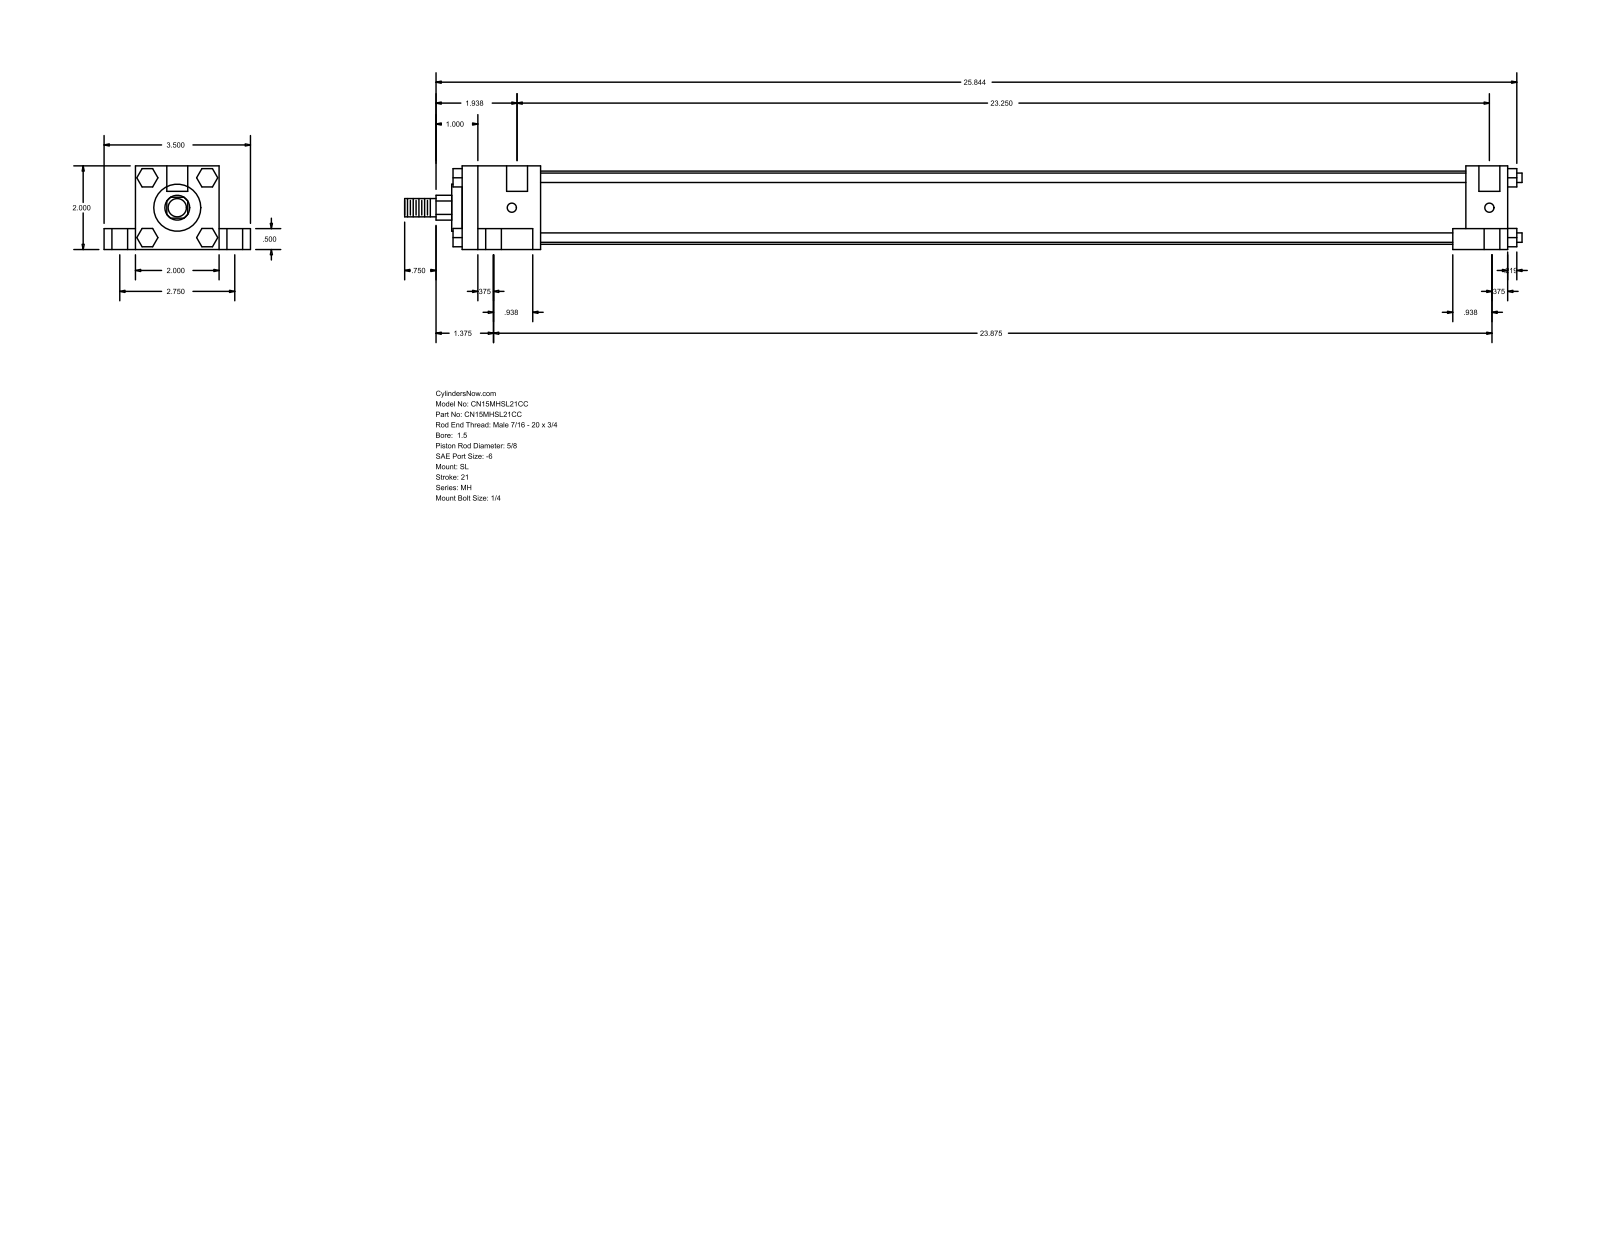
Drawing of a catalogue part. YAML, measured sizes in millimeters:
part_name: "MH_SL__0150_0.625"
step_written_by: "GSSL Pune (CONFIG_CONTROL_DESIGN)"
units: millimeters
bodies: {solids: 0, faces: 148, planar: 112, cylindrical: 36, other: 0}
overall_size: [678.66, 88.9, 50.8]
round_holes:
  - {diameter: 5.56, count: 4}
  - {diameter: 9.53, count: 4}
  - {diameter: 15.88, count: 4}
  - {diameter: 12.7, count: 2}
round_bosses_or_shafts:
  - {diameter: 5.71, count: 4}
  - {diameter: 44.45, count: 1}
  - {diameter: 28.57, count: 1}
  - {diameter: 15.88, count: 1}
  - {diameter: 11.11, count: 1}
partial_cylinders:
  - {radius: 7.54, count: 1}
face_to_face_distances: [50.8, 38.1, 19.05, 12.7, 69.85, 635, 25.4, 9.52, 33.34, 592.14]
hole_center_spacings: [34.96, 36.65, 37.73, 69.84, 593.17, 593.72, 596.33, 605.85]
